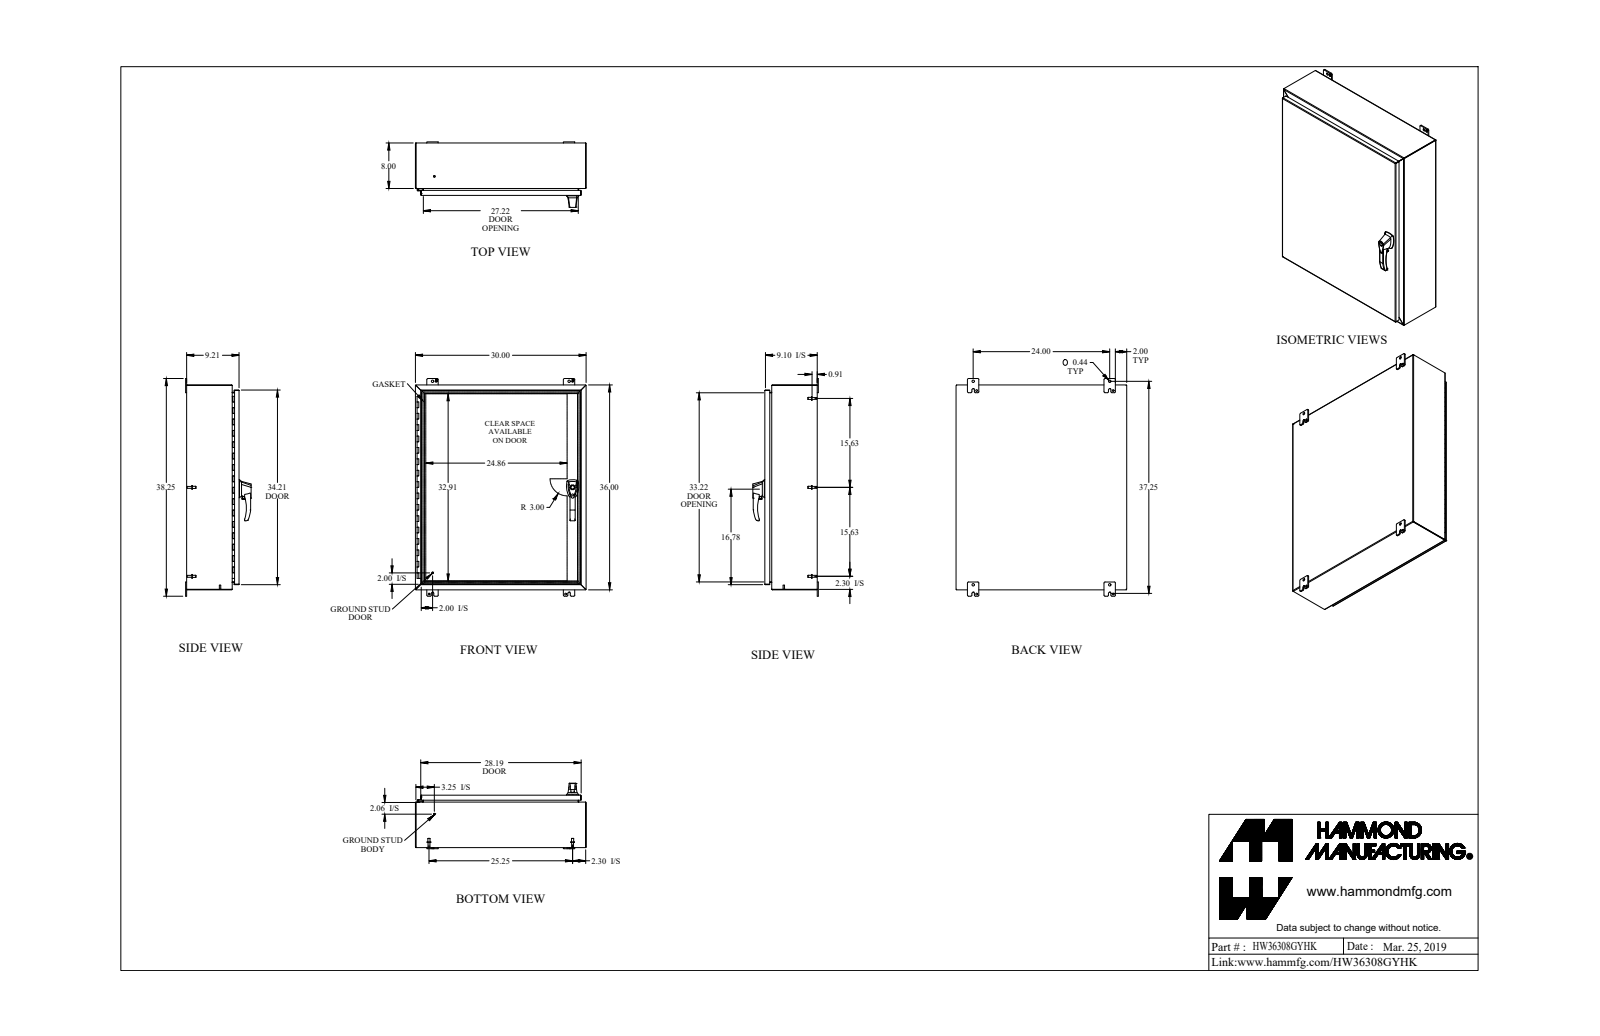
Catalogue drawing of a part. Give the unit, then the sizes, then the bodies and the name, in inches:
Units: inches
Overall size (bounding box): 38.25 × 30 × 11.512
Round holes (diameter × count): ⌀0.176 ×6, ⌀0.25 ×4, ⌀0.313 ×4, ⌀0.196 ×3, ⌀0.265 ×3, ⌀0.413 ×3, ⌀0.256 ×2, ⌀0.394 ×2, ⌀0.437 ×2, ⌀0.187 ×1, ⌀0.233 ×1, ⌀0.334 ×1
Round bosses / shafts (diameter × count): ⌀0.375 ×11, ⌀0.65 ×6, ⌀0.33 ×6, ⌀0.25 ×6, ⌀0.156 ×6, ⌀1 ×3, ⌀0.63 ×2, ⌀0.51 ×2
Partial cylindrical surfaces — rounded edges, fillets, slot ends (radius × count): R0.188 ×36, R0.25 ×27, R0.036 ×20, R0.108 ×20, R0.06 ×12, R0.116 ×12, R0.125 ×9, R0.045 ×8
Main face-to-face distances: 0.072, 0.072, 9.138, 9.066, 9.21, 9.138, 29.928, 35.928, 7.928, 29.856
Hole centre spacings: 14.118, 14.119, 28.237, 1.111, 11.578, 14.119, 24, 24.721
Volume: 310.3 in³ · Surface area: 8 164 in²
Bodies: 46 solids, 1615 faces (789 planar, 653 cylindrical, 173 other)
Part name (STEP PRODUCT): HW36308GYHK
STEP written by: SolidWorks 2018 (AUTOMOTIVE_DESIGN)
